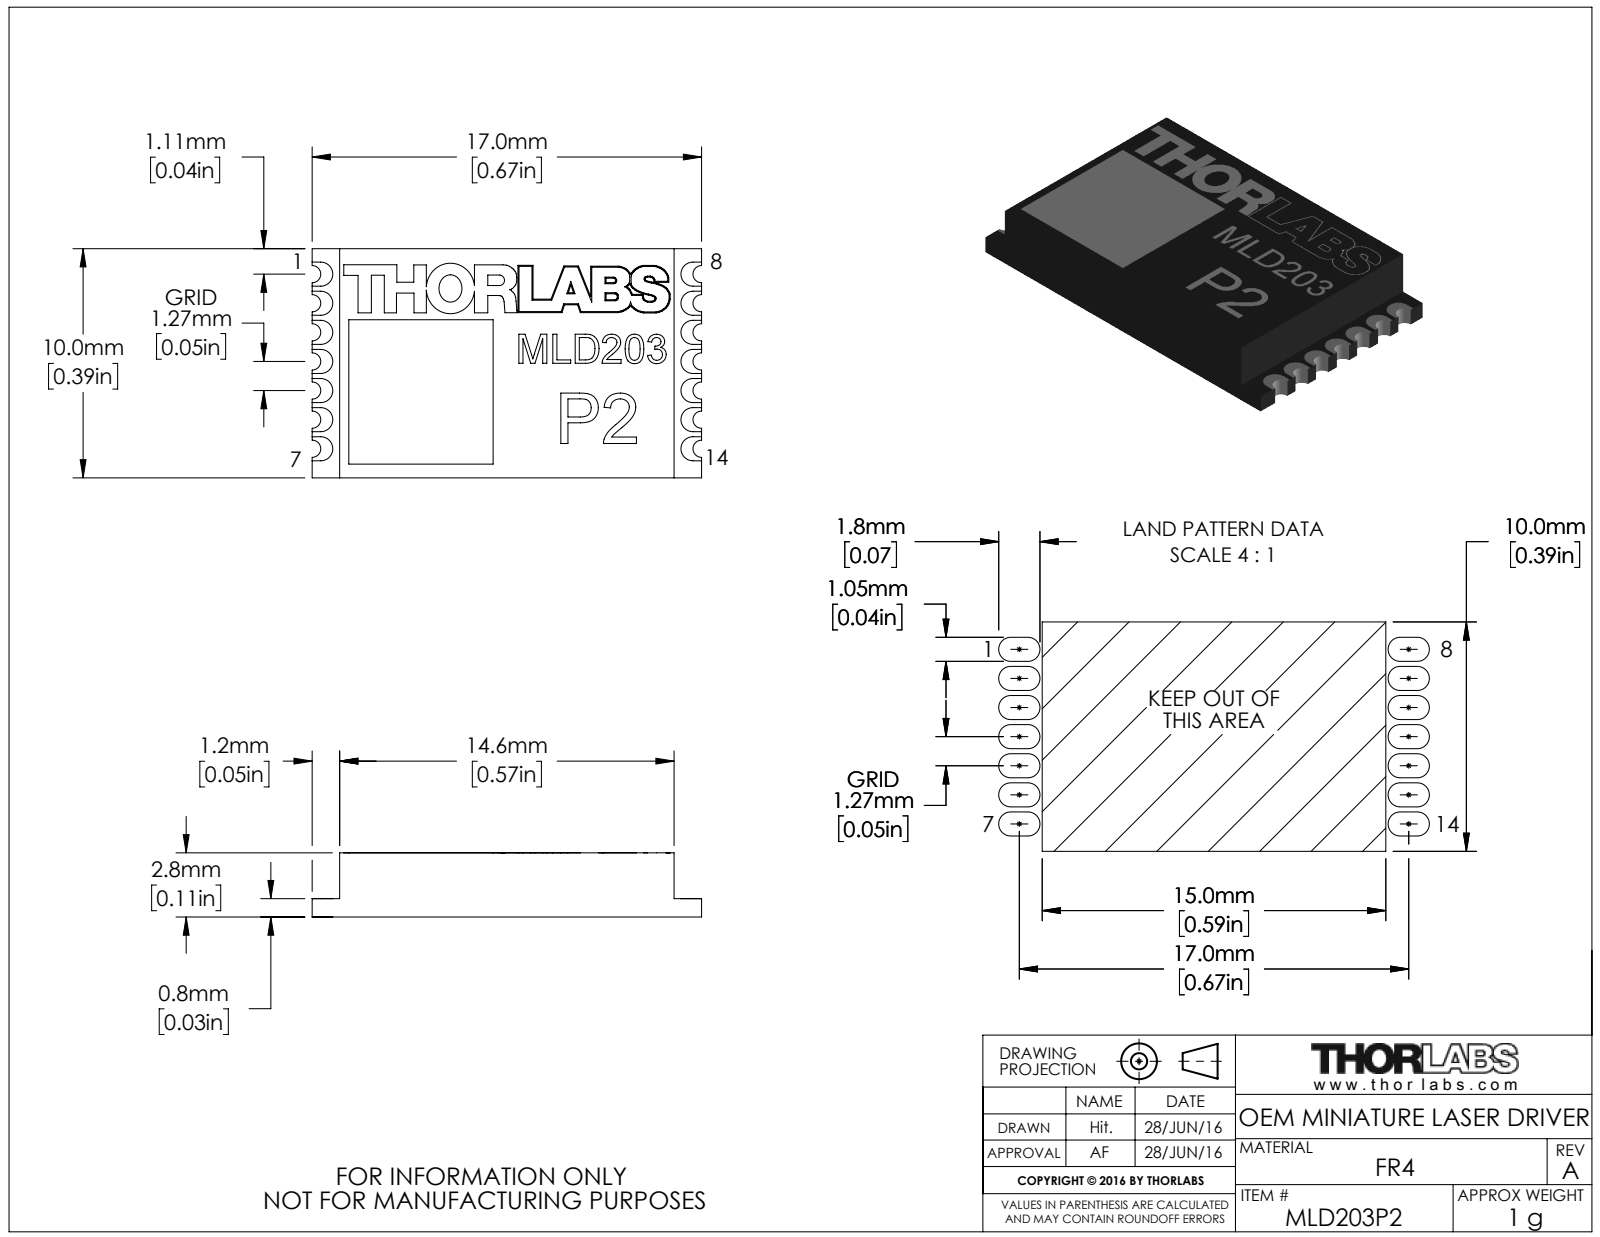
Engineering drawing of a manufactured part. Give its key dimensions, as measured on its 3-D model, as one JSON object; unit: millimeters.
{"part_name": "MTN006813-E0W", "step_written_by": "SolidWorks 2016 (AUTOMOTIVE_DESIGN)", "units": "millimeters", "bodies": {"solids": 1, "faces": 640, "planar": 520, "cylindrical": 56, "other": 64}, "overall_size": [17, 10, 2.8], "volume_mm3": 426, "surface_area_mm2": 480, "partial_cylinders_radius": [[0.38, 14], [0.53, 14]], "face_to_face_distances": [2.8, 10, 0.8, 2, 14.6, 1.2, 15.8, 17, 6.3, 7.9]}
